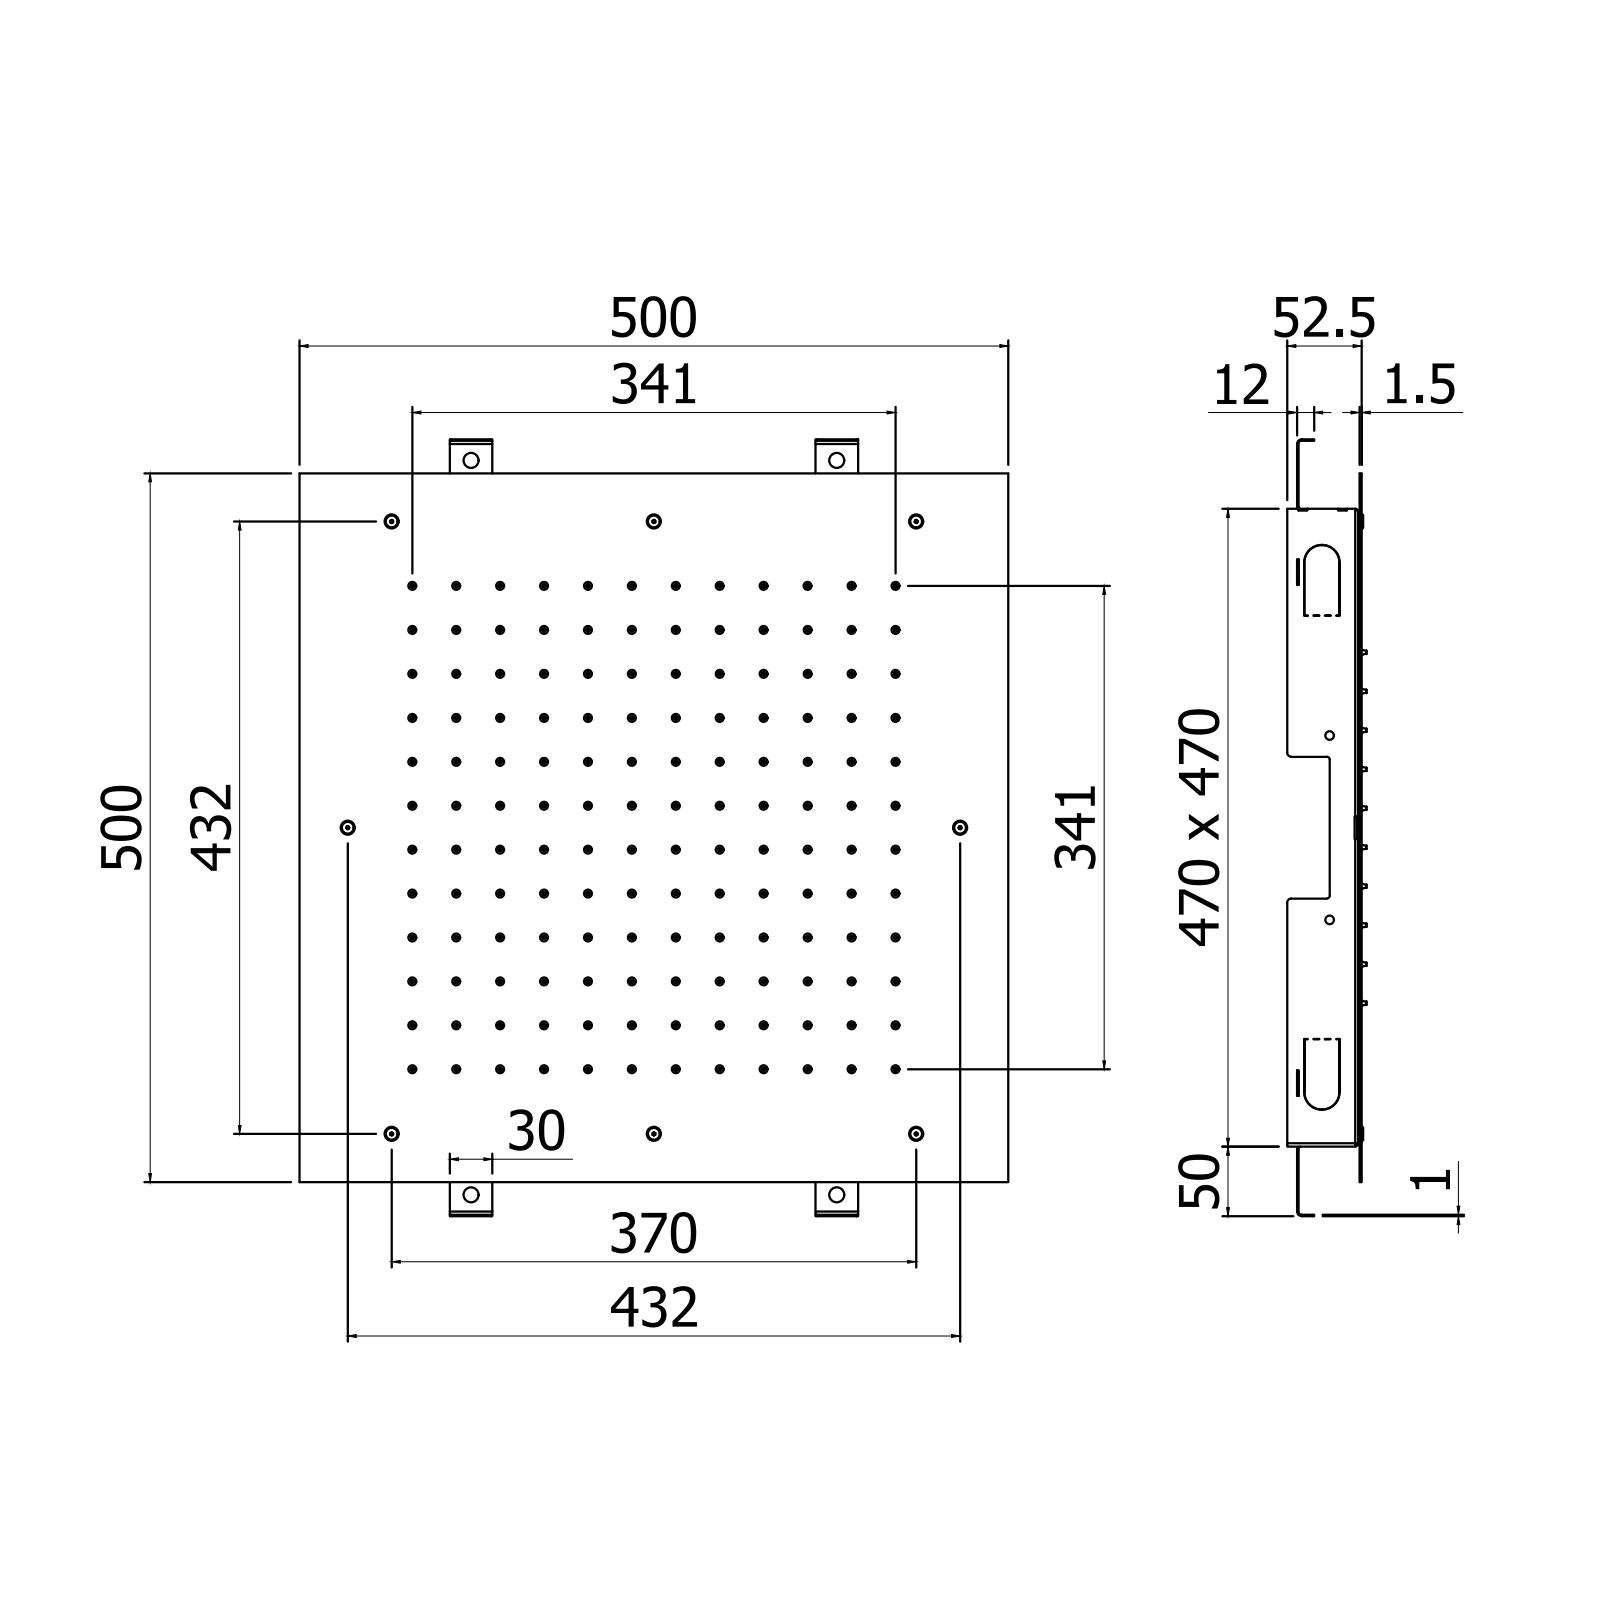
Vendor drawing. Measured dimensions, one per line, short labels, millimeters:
name: ZSOF301CR
written by: CREO PARAMETRIC BY PTC INC, 2020044 (CONFIG_CONTROL_DESIGN)
unit: mm
bodies: 145 solids, 2530 faces (366 planar, 676 cylindrical, 1488 other)
size: 500 × 500 × 4.8
volume: 375 902 mm³; area: 514 855 mm²
holes: 144× ⌀1.5, 144× ⌀5, 8× ⌀7
bosses: 8× ⌀10, 8× ⌀5
rounds: 48× R0.2, 4× R2
face distances: 1.5, 500, 2.5, 1, 4.8, 3.3, 2.3, 2, 384.5, 208
hole spacings: 31, 69.32, 43.84, 62, 98.03, 127.82, 158.07, 93
